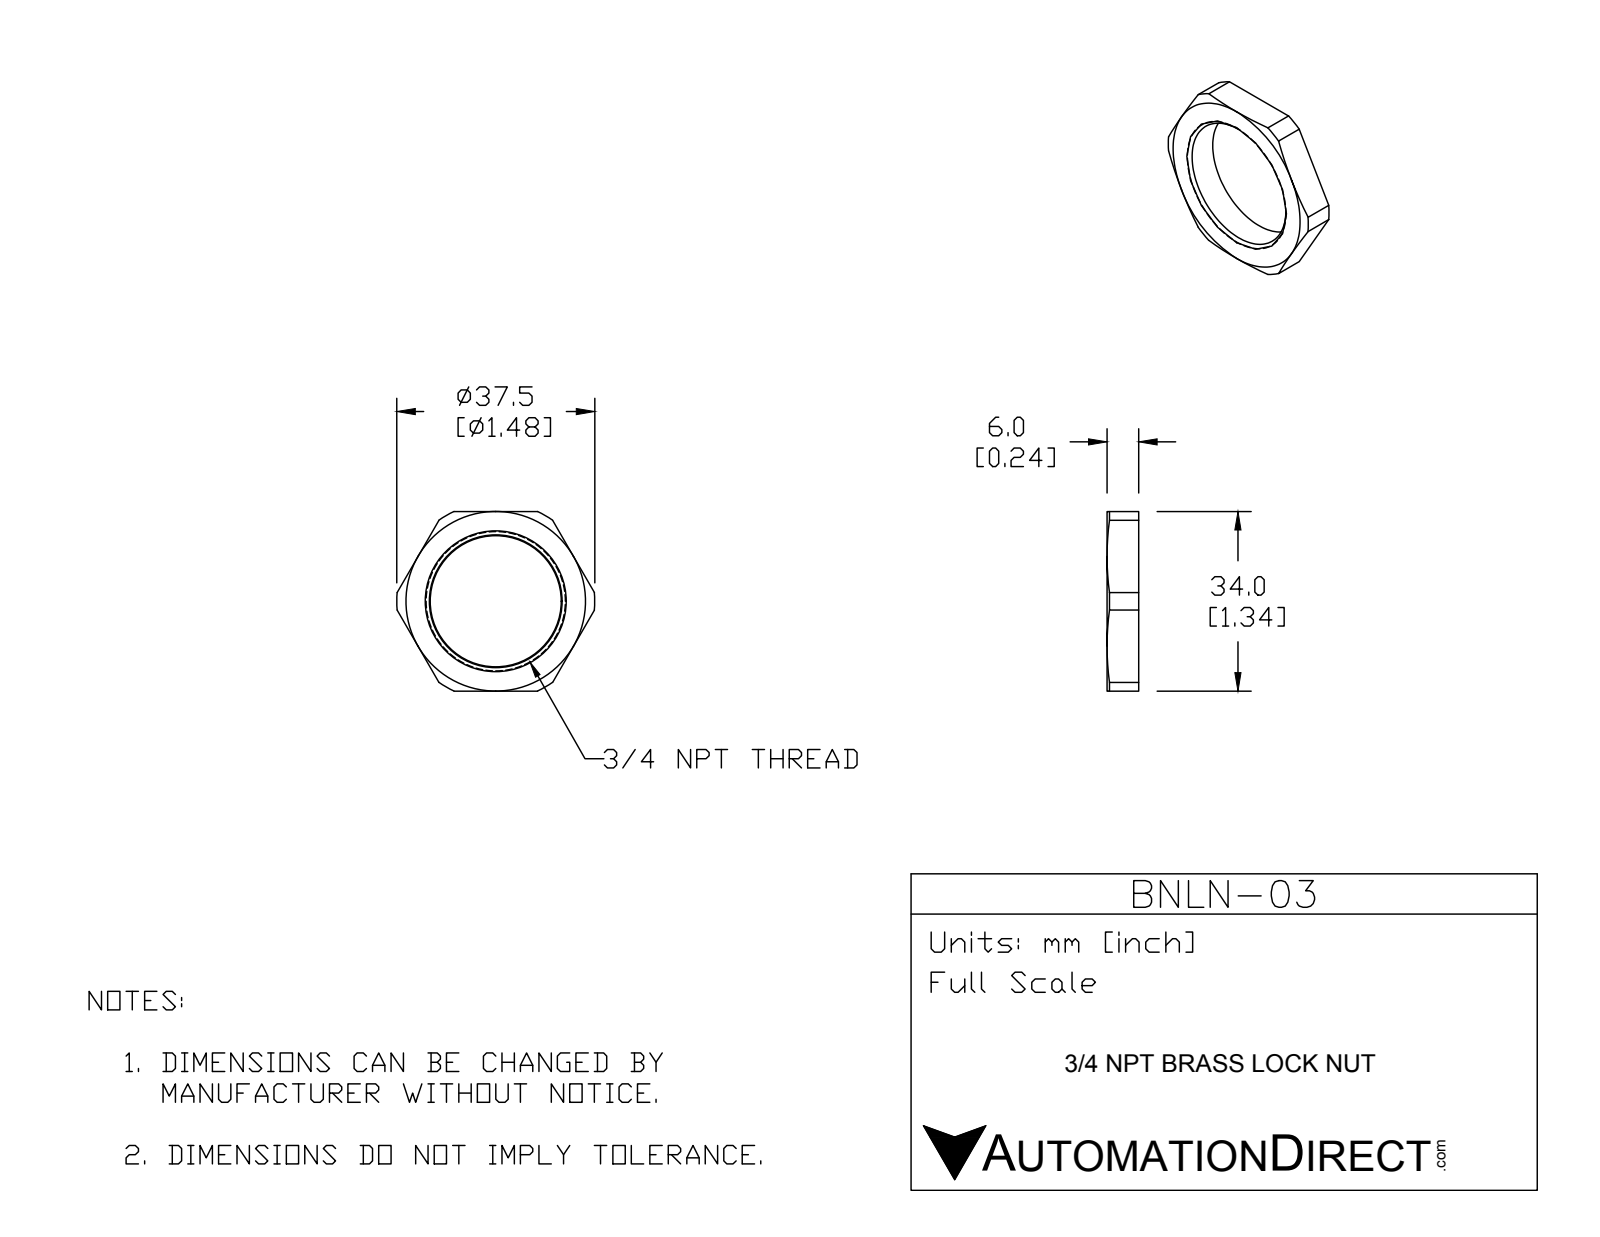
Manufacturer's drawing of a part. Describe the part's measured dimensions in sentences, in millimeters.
The part is named "BNLN-03". Its 3-D file was written by "SolidWorks 2015 (CONFIG_CONTROL_DESIGN)". It is 1 solid with 25 faces: 8 planar, 7 cylindrical and 10 other. Overall it measures 37.5 by 34 by 6 millimeters. Its volume is 2 986 cubic millimeters and its surface area 2 116 square millimeters. Partial cylindrical surfaces (rounded edges, fillets, slot ends): 1 of radius 18.75. The main face-to-face distances are 6, 34.
